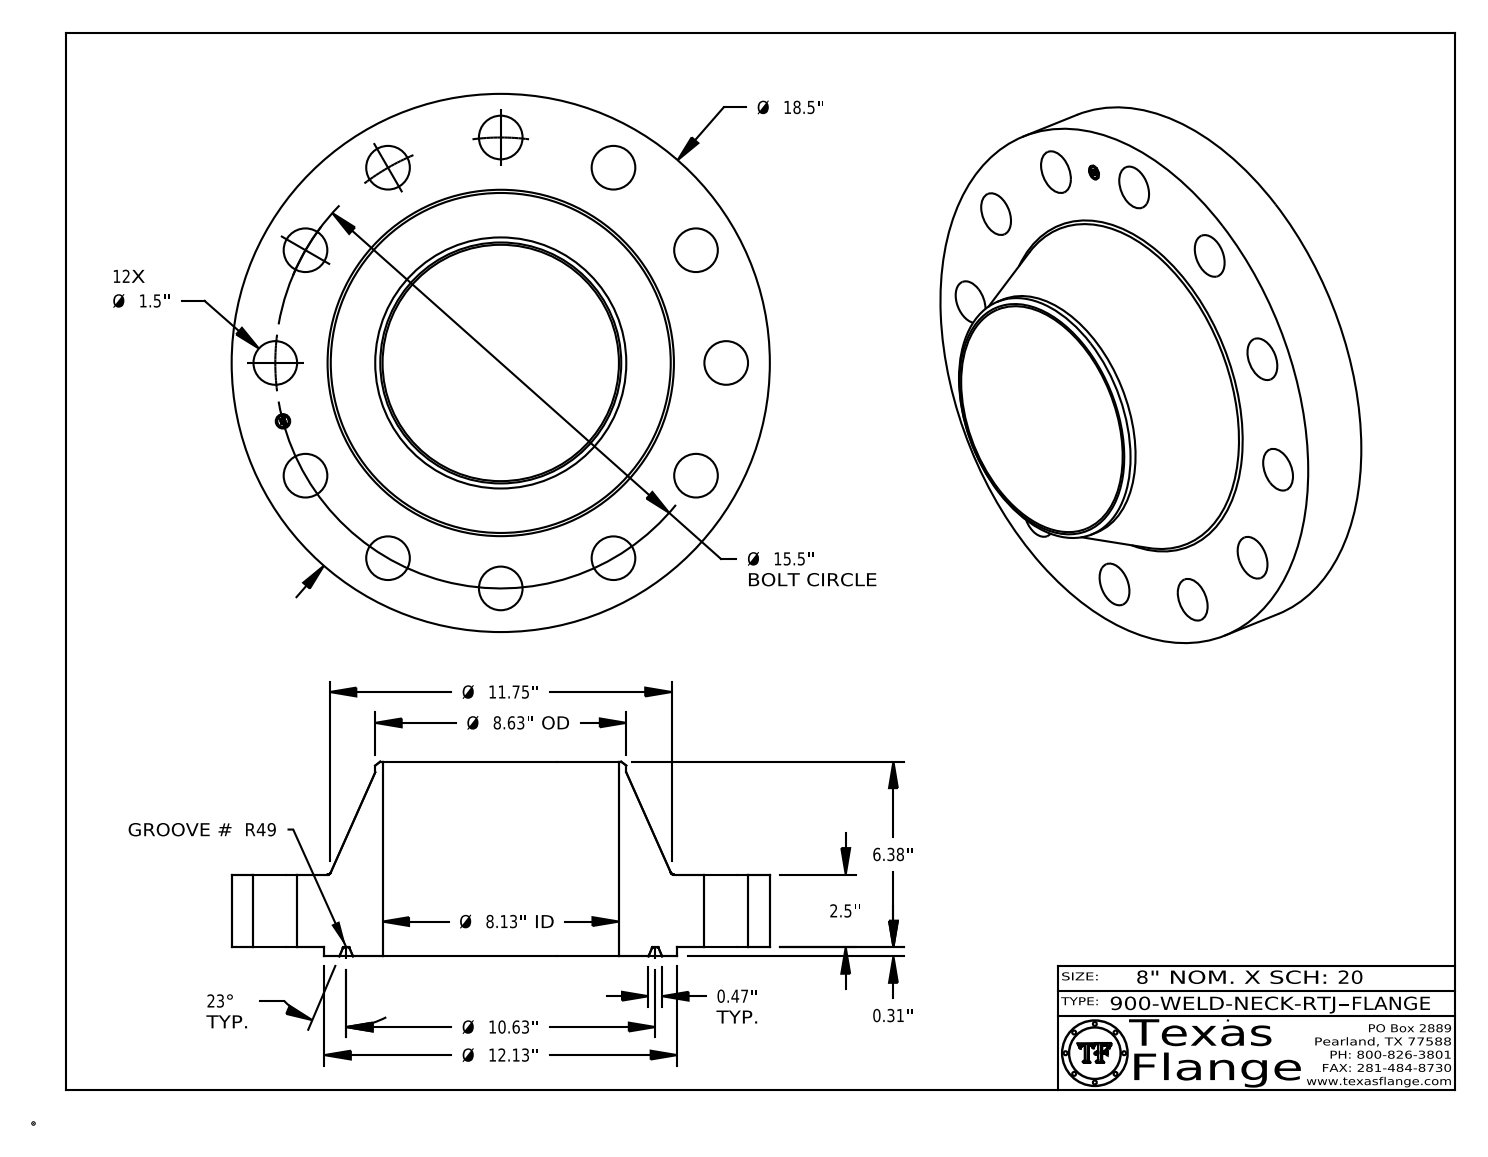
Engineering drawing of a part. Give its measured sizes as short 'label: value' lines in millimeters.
name: 900-WELD-NECK-RTJ
written by: CATIA V5 STEP AP214 (AUTOMOTIVE_DESIGN)
unit: mm
bodies: 1 solid, 437 faces (371 planar, 52 cylindrical, 14 other)
size: 469.9 × 469.9 × 170
volume: 10 070 000 mm³; area: 615 800 mm²
holes: 12× ⌀38.1, 1× ⌀12.6, 1× ⌀206.4
bosses: 8× ⌀0.8, 1× ⌀469.9, 1× ⌀308, 1× ⌀219.2, 1× ⌀9.9
face distances: 63.5, 8, 71.5, 170, 162.1, 98.6, 0.4, 71.1, 63.1, 98.9
hole spacings: 196.9, 196.9, 341, 101.9, 278.4, 380.3, 101.9, 278.4
